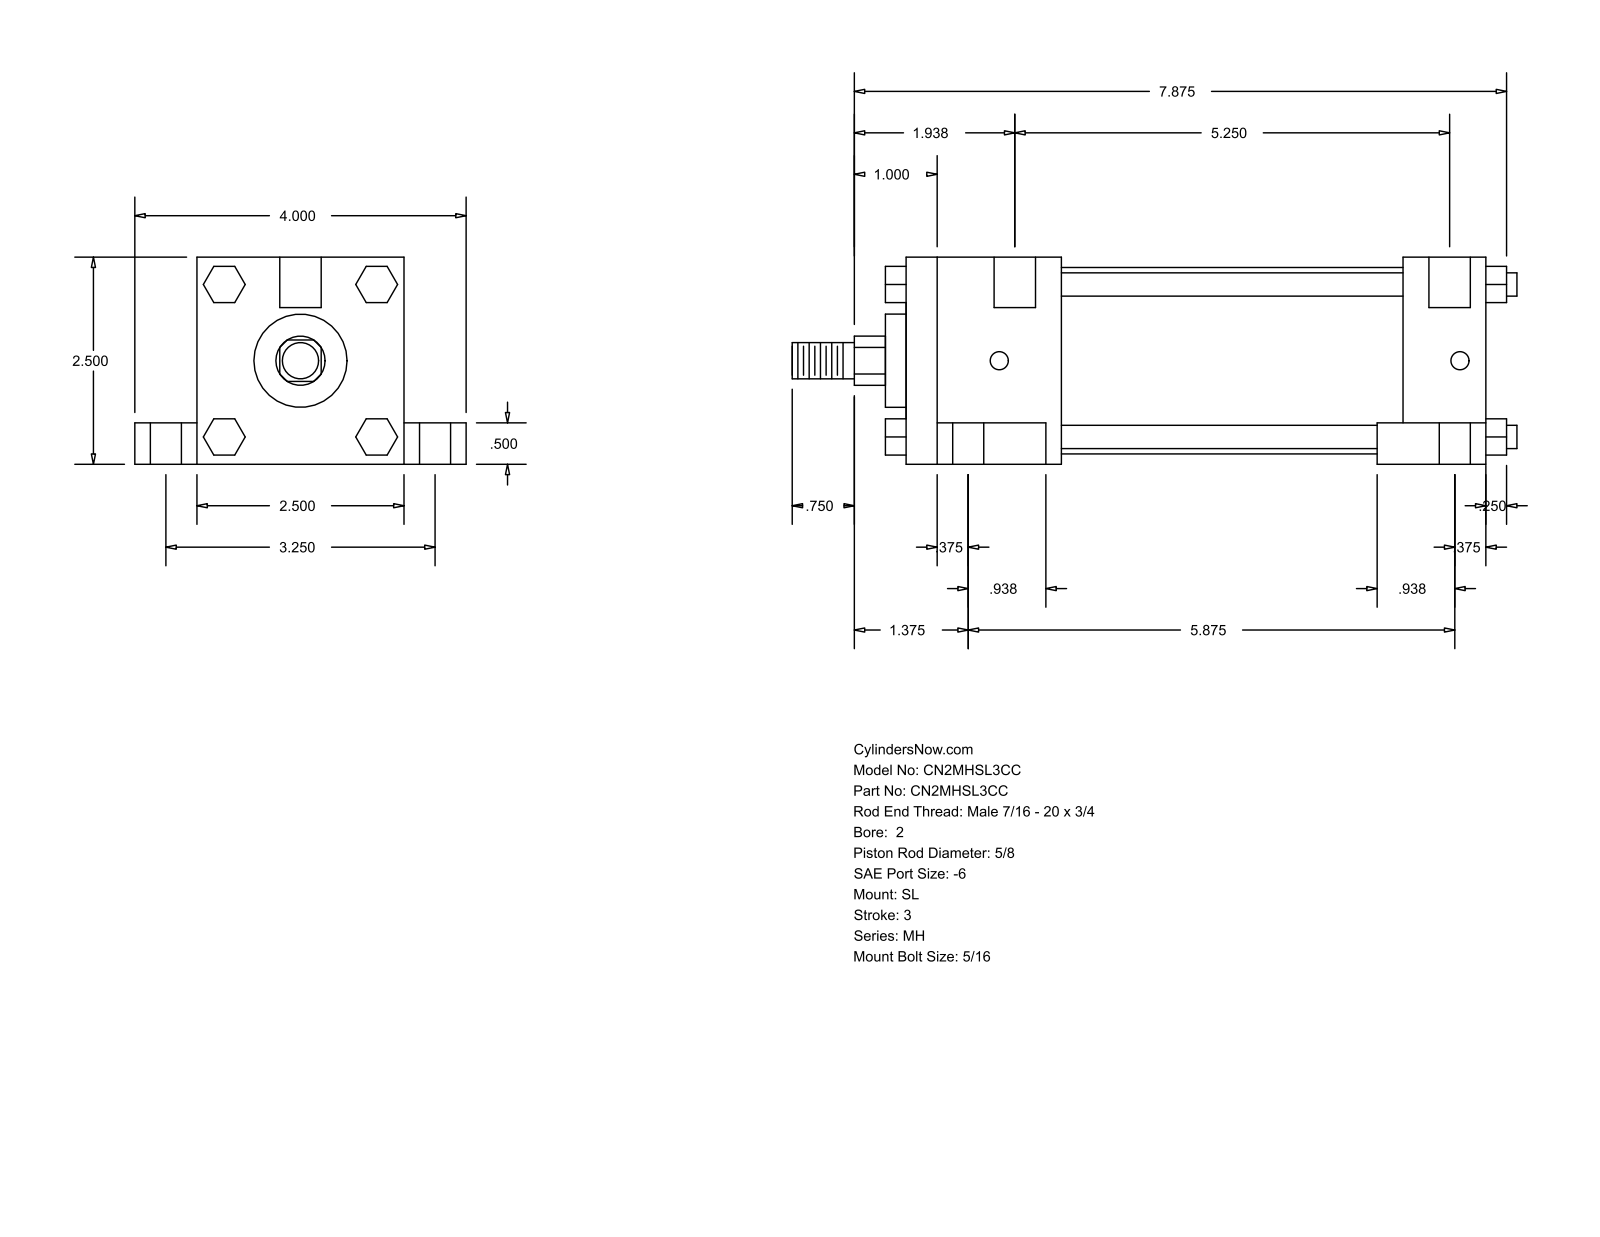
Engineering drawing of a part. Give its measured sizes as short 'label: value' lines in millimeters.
name: MH_SL__0200_0.625
written by: GSSL Pune (CONFIG_CONTROL_DESIGN)
unit: mm
bodies: 0 solids, 148 faces (112 planar, 36 cylindrical, 0 other)
size: 222.25 × 101.6 × 63.5
holes: 4× ⌀5.56, 4× ⌀9.53, 4× ⌀15.88, 2× ⌀12.7
bosses: 4× ⌀7.14, 1× ⌀57.15, 1× ⌀28.57, 1× ⌀15.88, 1× ⌀11.11
rounds: 1× R7.54
face distances: 63.5, 177.8, 12.7, 19.05, 82.55, 50.8, 25.4, 101.6, 152.4, 47.62
hole spacings: 41.3, 42.36, 43.67, 82.54, 141.11, 141.29, 145.67, 149.23
